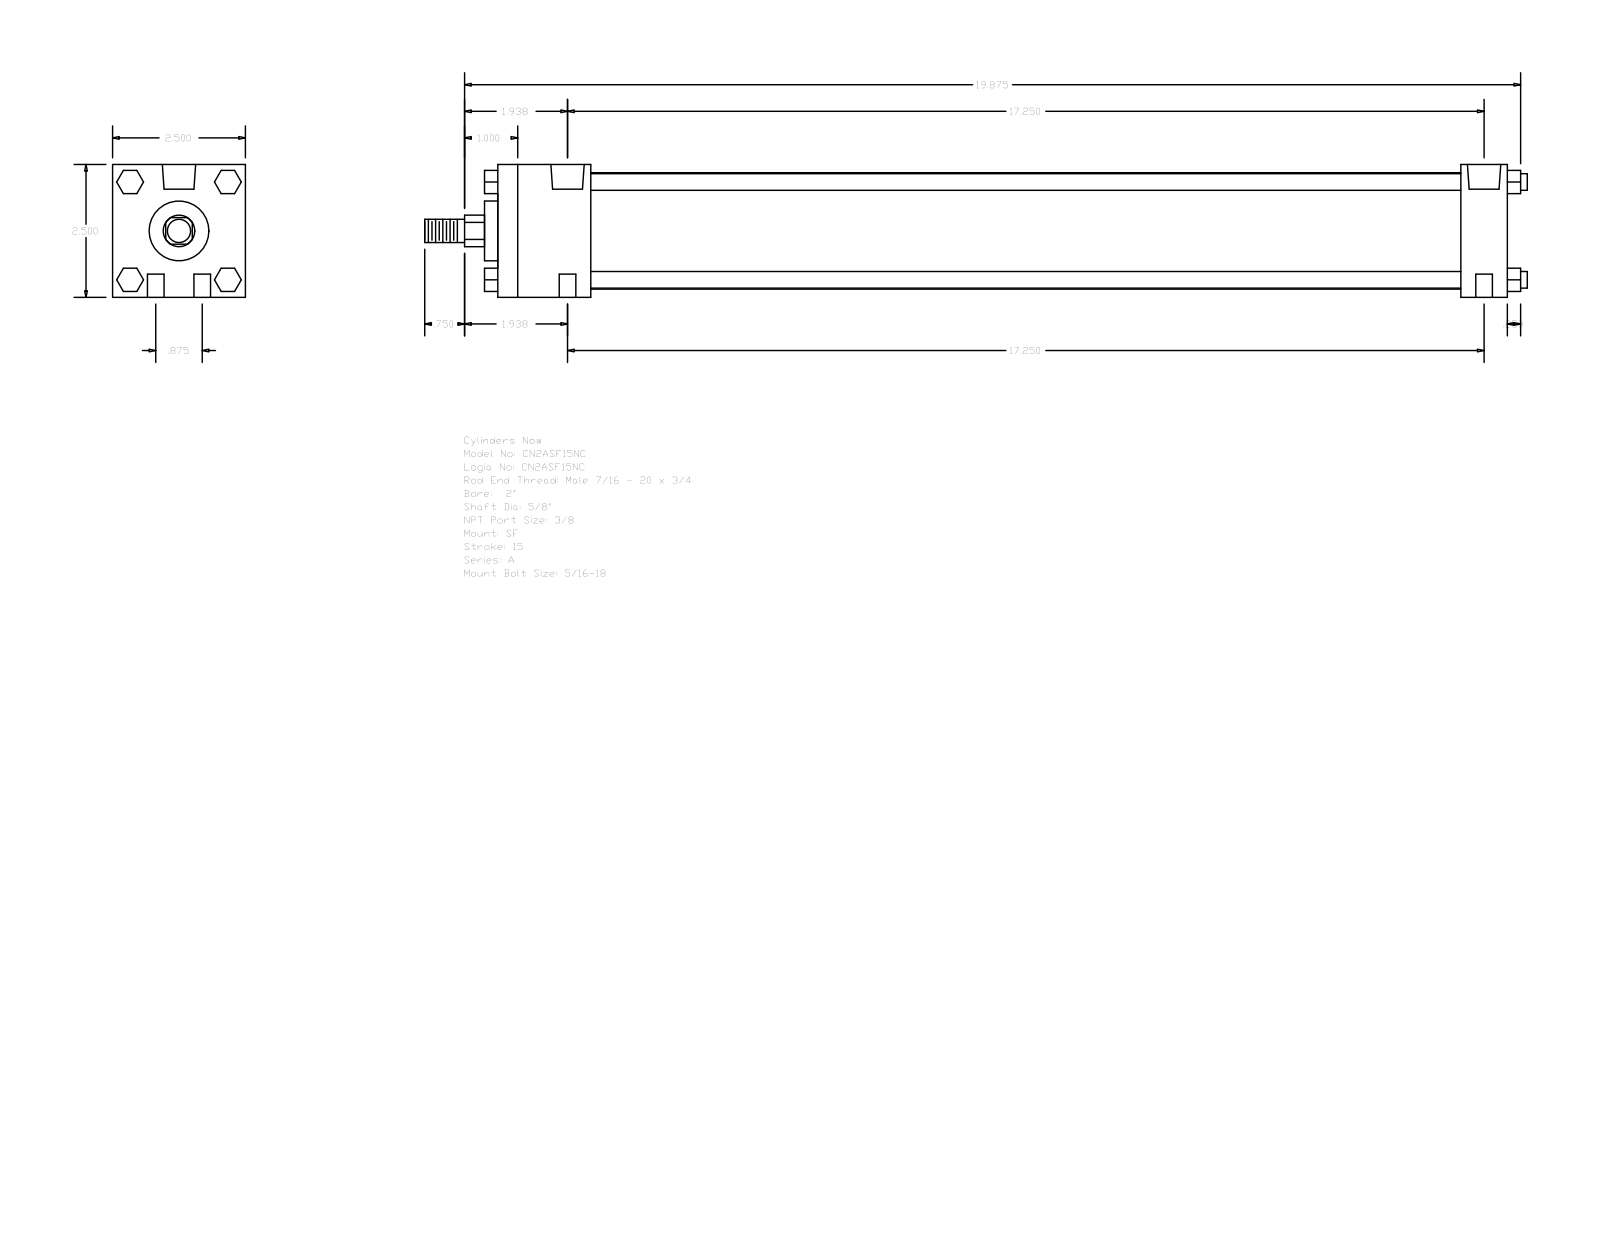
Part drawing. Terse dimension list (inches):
name: A_SF__0200_0.625
written by: GSSL Pune (CONFIG_CONTROL_DESIGN)
unit: in
bodies: 0 solids, 124 faces (94 planar, 30 cylindrical, 0 other)
size: 20.75 × 2.5 × 2.5
holes: 4× ⌀0.313, 2× ⌀0.219, 2× ⌀0.627
bosses: 4× ⌀0.313, 1× ⌀2.19, 1× ⌀1.125, 1× ⌀0.625, 1× ⌀0.437
rounds: 1× R0.297
face distances: 2.5, 19, 18.125, 0.875, 1.75, 16.375, 17.25, 2, 0.25, 18.375
hole spacings: 0.437, 17.256, 17.25, 0.875, 17.272, 16.937
